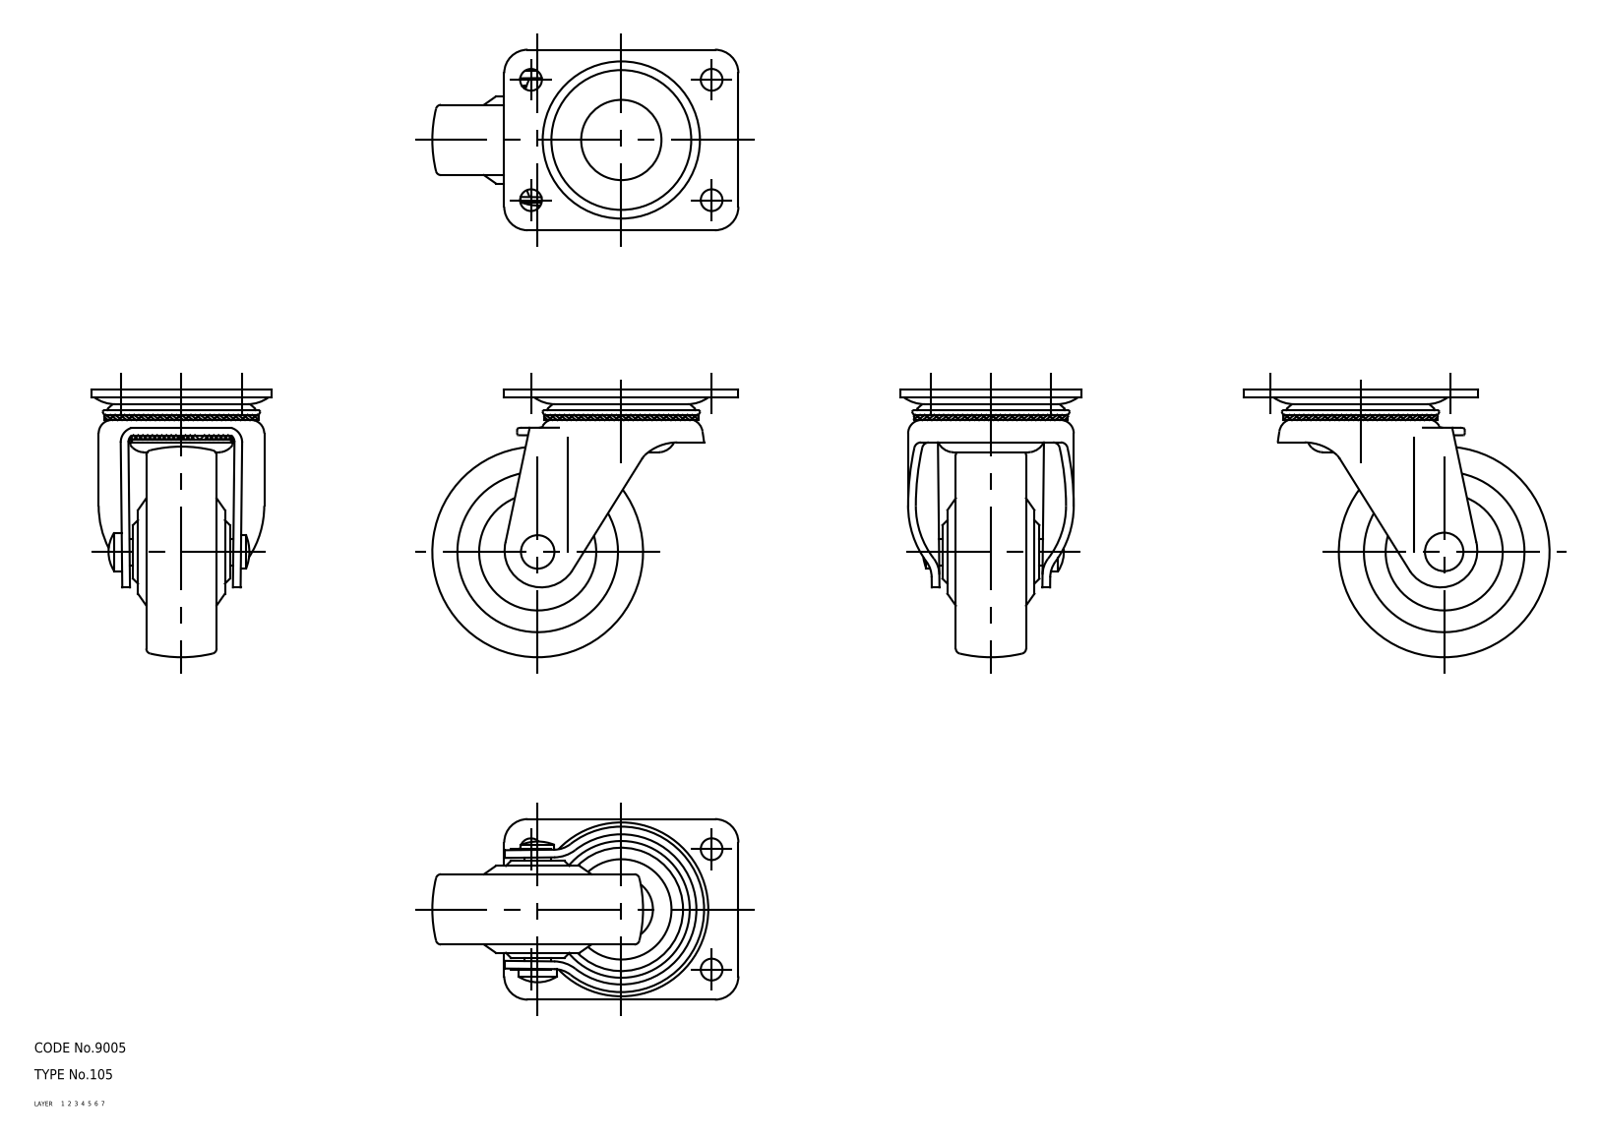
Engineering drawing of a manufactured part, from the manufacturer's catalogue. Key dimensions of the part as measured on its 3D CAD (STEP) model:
Part name (STEP PRODUCT): wheel; mounting plate; main shaft; axle (+1 more)
STEP written by: CADfix (AUTOMOTIVE_DESIGN)
Units: millimetres
Bodies: 5 solids, 226 faces (0 planar, 0 cylindrical, 226 other)
Overall size (bounding box): 91.5 × 80 × 54
Volume: 101 015 mm³ · Surface area: 35 063 mm²
